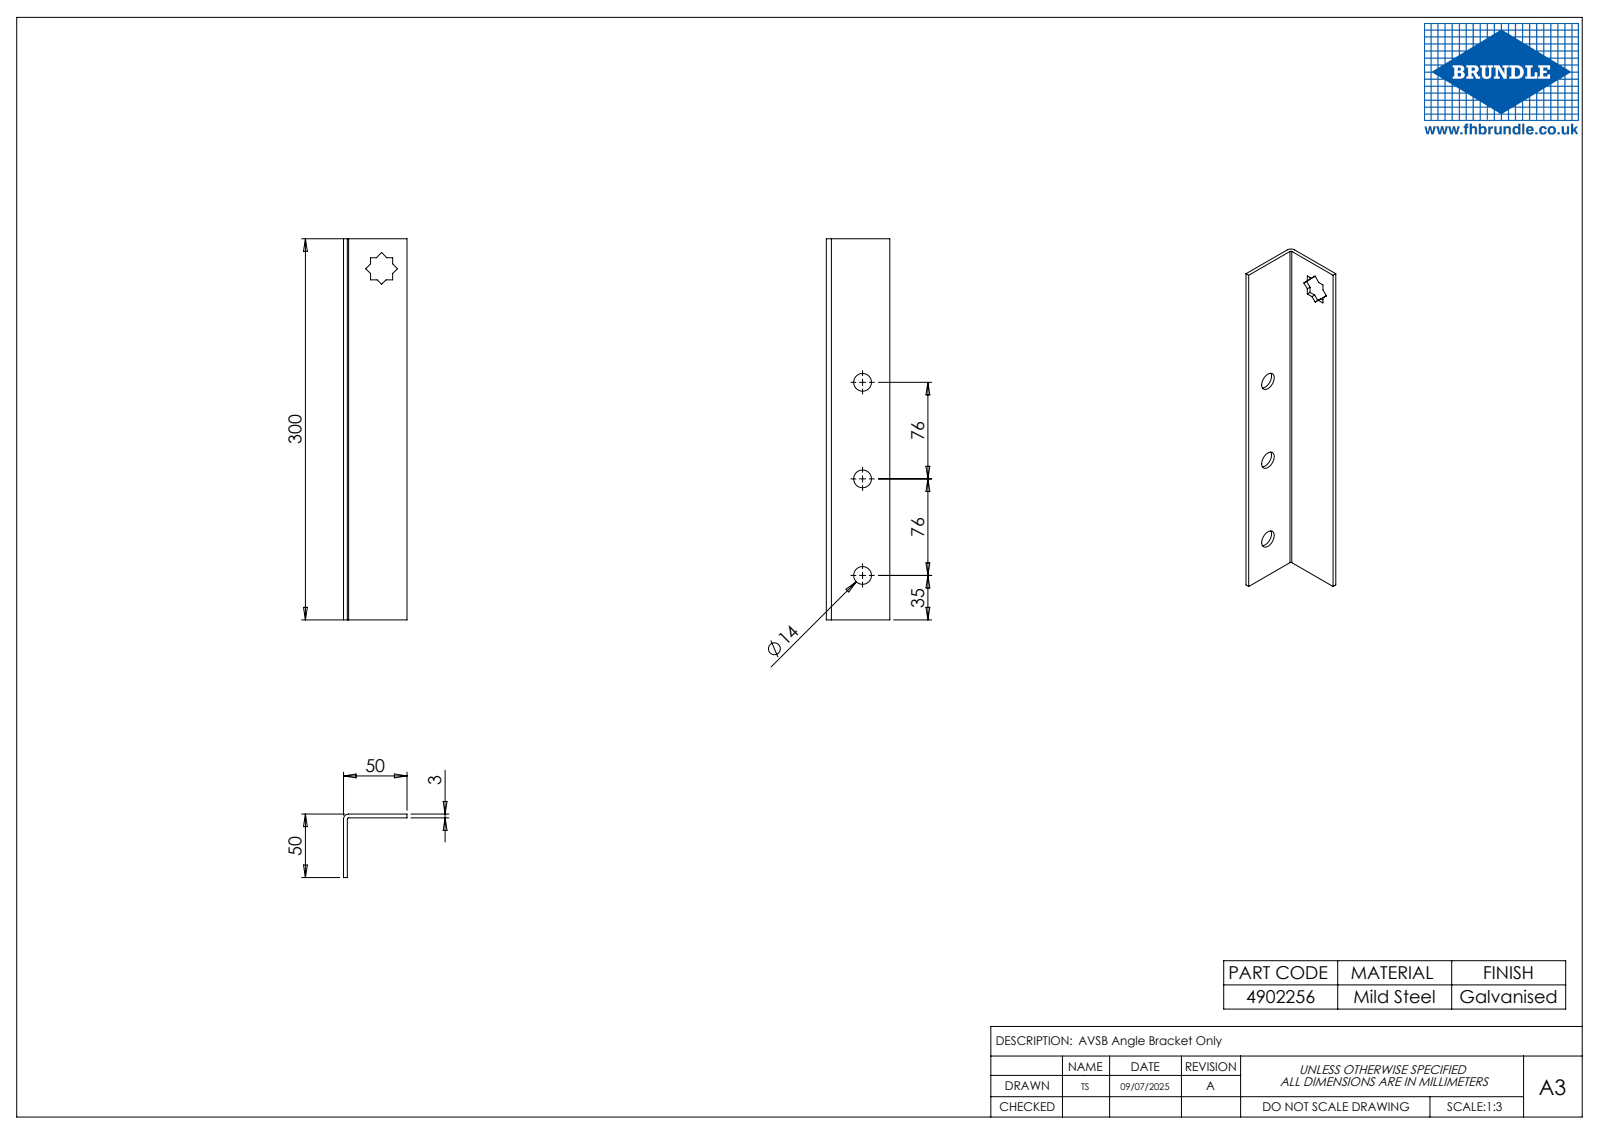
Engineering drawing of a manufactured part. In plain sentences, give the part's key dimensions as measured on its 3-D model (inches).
The part is named "4902256". Its 3-D file was written by "SolidWorks 2023 (CONFIG_CONTROL_DESIGN)". It is 1 solid with 32 faces: 24 planar, 8 cylindrical and 0 other. Overall it measures 11.811 by 1.969 by 1.969 inches. Its volume is 5.118 cubic inches and its surface area 91.34 square inches. Round holes: 3 of diameter 0.551. Partial cylindrical surfaces (rounded edges, fillets, slot ends): 1 of radius 0.039, 1 of radius 0.157. The main face-to-face distances are 0.118, 1.969, 1.85, 11.811, 0.685, 10.537, 1.274, 0.839, 1.524, 0.72. The hole center spacings are 2.992, 5.984.
